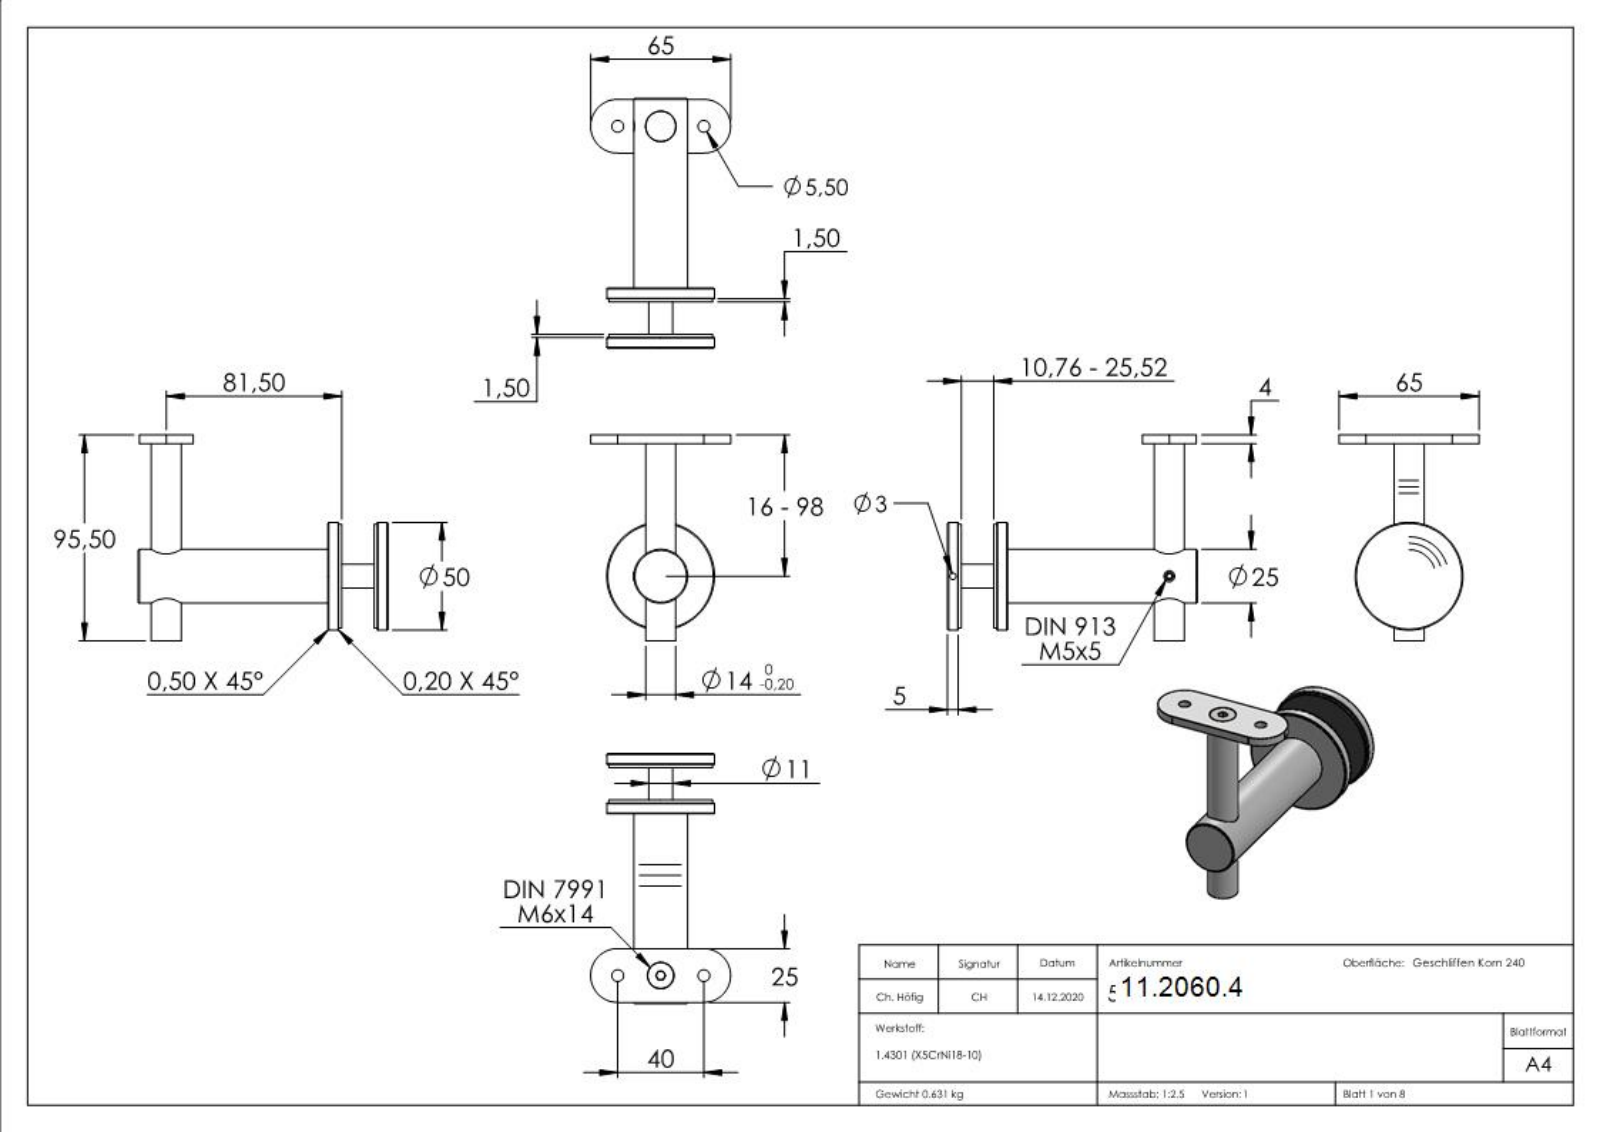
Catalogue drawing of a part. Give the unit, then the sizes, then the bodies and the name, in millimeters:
Units: millimetres
Overall size (bounding box): 116 × 95.5 × 88
Round holes (diameter × count): ⌀5.5 ×2, ⌀3 ×1, ⌀4.2 ×1, ⌀5 ×1, ⌀6.8 ×1, ⌀8 ×1, ⌀8.1 ×1, ⌀11.5 ×1, ⌀12.4 ×1, ⌀14.2 ×1
Round bosses / shafts (diameter × count): ⌀50 ×1, ⌀48 ×1, ⌀25 ×1, ⌀14 ×1, ⌀12 ×1, ⌀11 ×1, ⌀6 ×1, ⌀5 ×1
Partial cylindrical surfaces — rounded edges, fillets, slot ends (radius × count): R12.5 ×2
Main face-to-face distances: 18, 1.5, 16.5, 5, 23, 6.5, 21.5, 15, 28, 4
Hole centre spacings: 20, 40, 100.5
Volume: 84 882 mm³ · Surface area: 36 260 mm²
Bodies: 9 solids, 321 faces (163 planar, 28 cylindrical, 130 other)
Part name (STEP PRODUCT): 503XX-240 Teil5_50350-240 Teil5; 503XX-240 Teil2_50350-240 Teil2; 50350-240; 503XX-240 Teil6 (+8 more)
STEP written by: SolidWorks 2015 (CONFIG_CONTROL_DESIGN)
